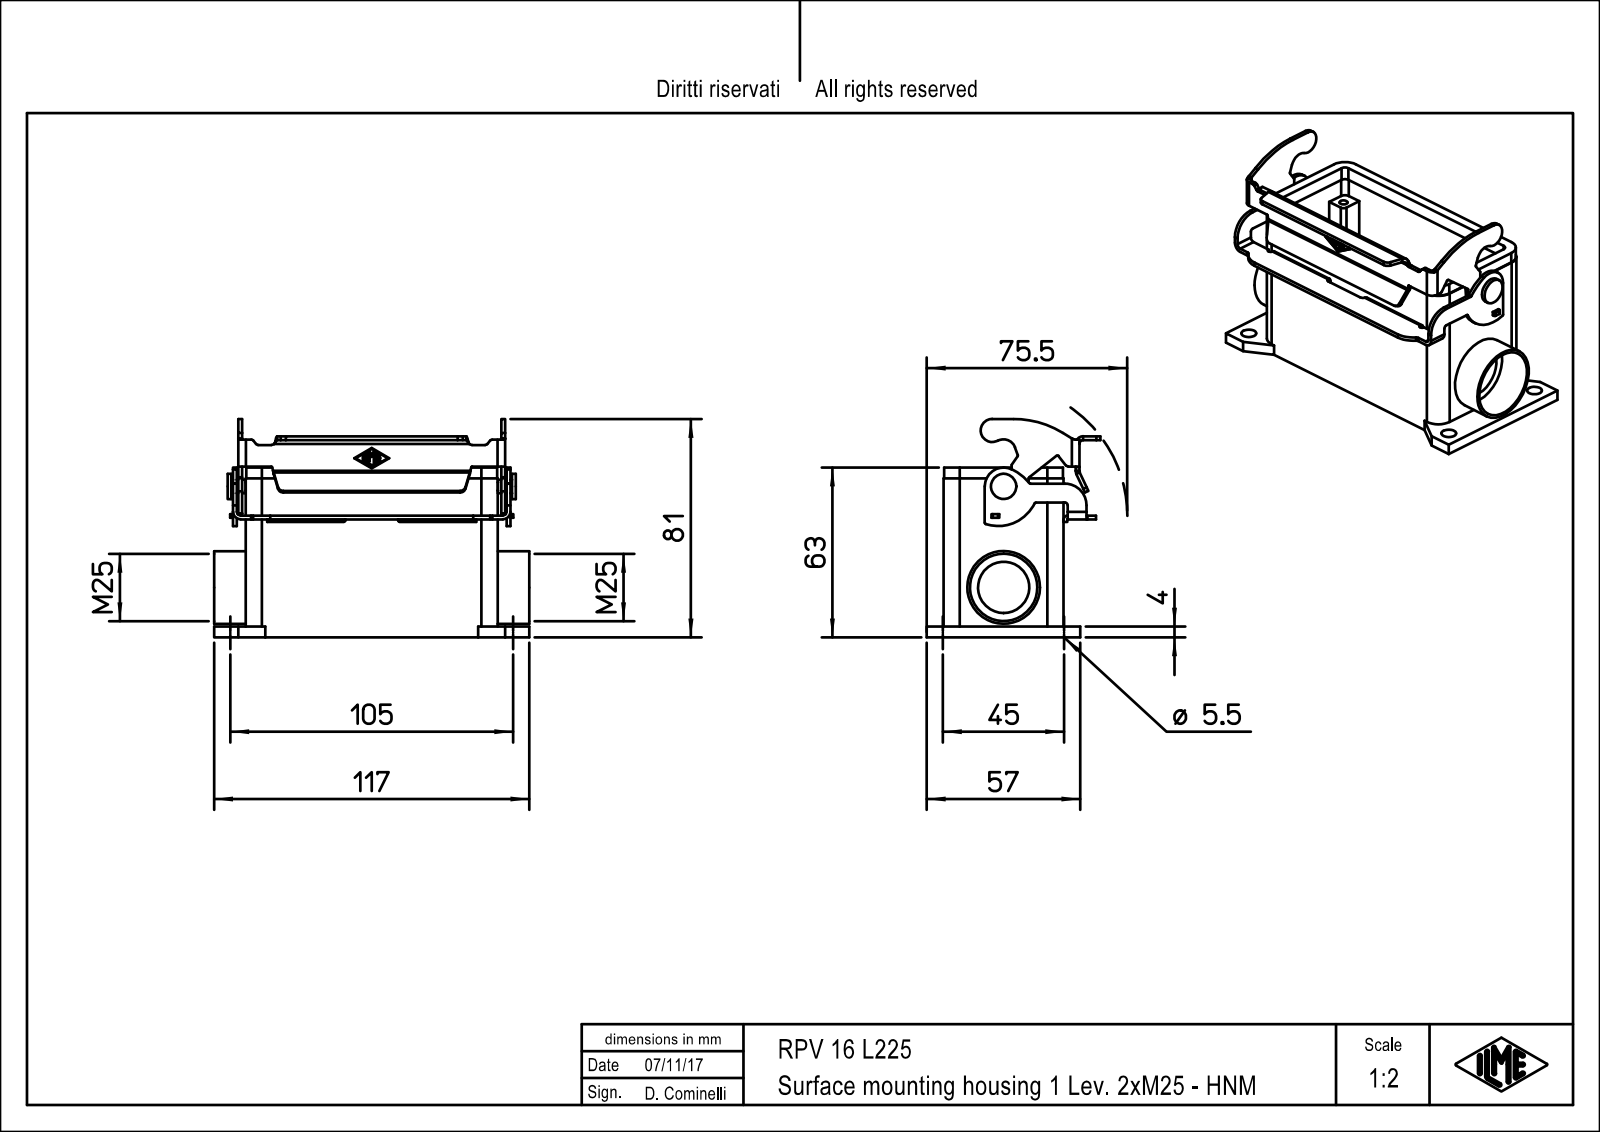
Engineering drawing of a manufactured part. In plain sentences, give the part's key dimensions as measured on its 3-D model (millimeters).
The part is named "RVP_16_L225". Its 3-D file was written by "PTC Creo Elements/Direct Modeling 19.0E 27-Jun-2016 (C) Parametric Technology GmbH (AUTOMOTIVE_DESIGN)". It is 1 solid with 380 faces: 198 planar, 170 cylindrical and 12 other. Overall it measures 117 by 81 by 64.48 millimeters. Its volume is 104 563 cubic millimeters and its surface area 58 876 square millimeters. Round holes: 4 of diameter 2.46, 4 of diameter 3, 4 of diameter 5.5, 1 of diameter 19, 1 of diameter 25. Round bosses or shafts: 1 of diameter 27, 1 of diameter 9.4, 1 of diameter 5, 1 of diameter 3. Partial cylindrical surfaces (rounded edges, fillets, slot ends): 16 of radius 0.25, 12 of radius 0.5, 12 of radius 1, 11 of radius 1.5, 8 of radius 2, 6 of radius 1.4, 6 of radius 2.8, 4 of radius 1.8. The main face-to-face distances are 4, 40.5, 1.4, 44.5, 36.5, 2, 99.6, 11.5, 82, 2.75. The hole center spacings are 16.43, 38.54, 91.69, 98.09, 27, 45, 77.5, 82.07.
